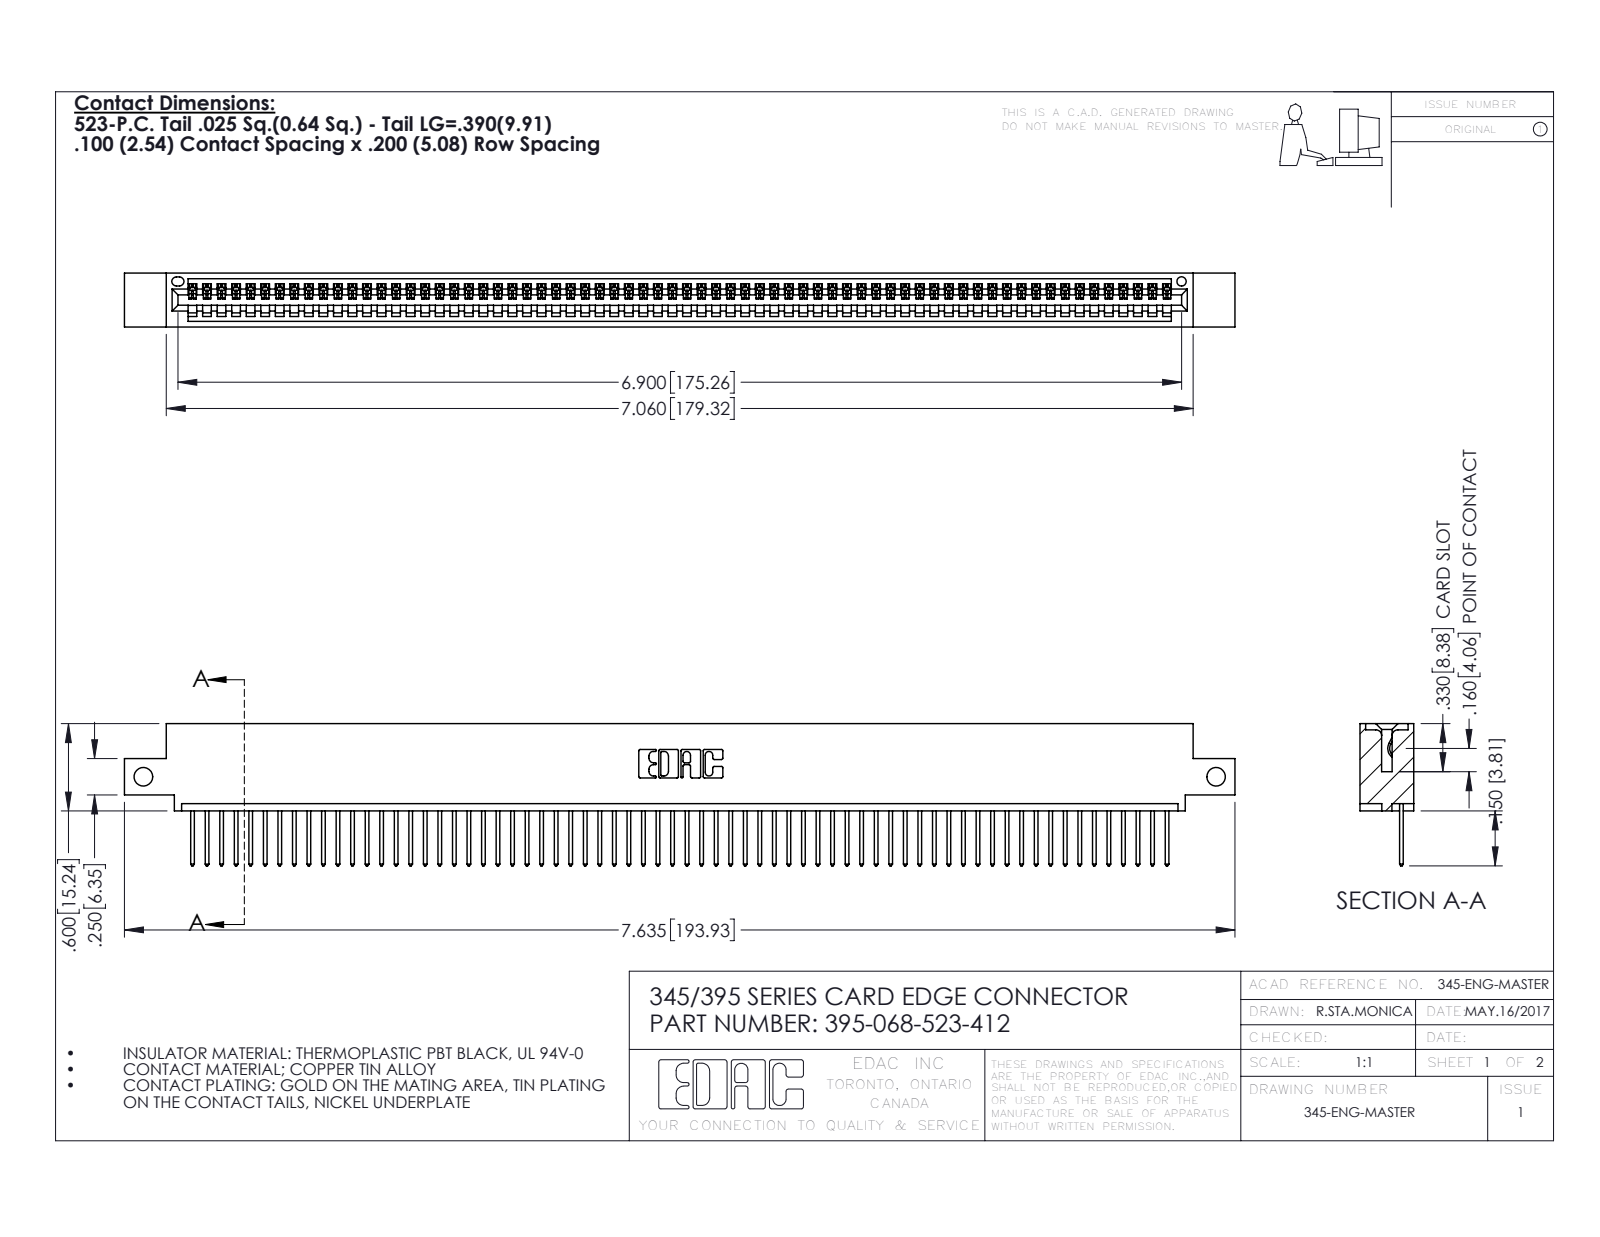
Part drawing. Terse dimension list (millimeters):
name: 345-292-001_345-293-123; 395-068-523-412; 345 Part_0.110 Offset - Side Mount
written by: SolidWorks 2016 (CONFIG_CONTROL_DESIGN)
unit: mm
bodies: 69 solids, 4074 faces (2804 planar, 1270 cylindrical, 0 other)
size: 193.9 × 24.8 × 9.4
volume: 18 450 mm³; area: 24 880 mm²
holes: 2× ⌀3.3, 1× ⌀1.6
rounds: 136× R0.2, 136× R0.3, 22× R0.3, 6× R0.2, 6× R0.8, 3× R0.7, 2× R0.8, 2× R1
face distances: 7.6, 1.8, 9.4, 2.5, 6.9, 0.6, 5.1, 5.7, 3.8, 1.8
hole spacings: 187.3
